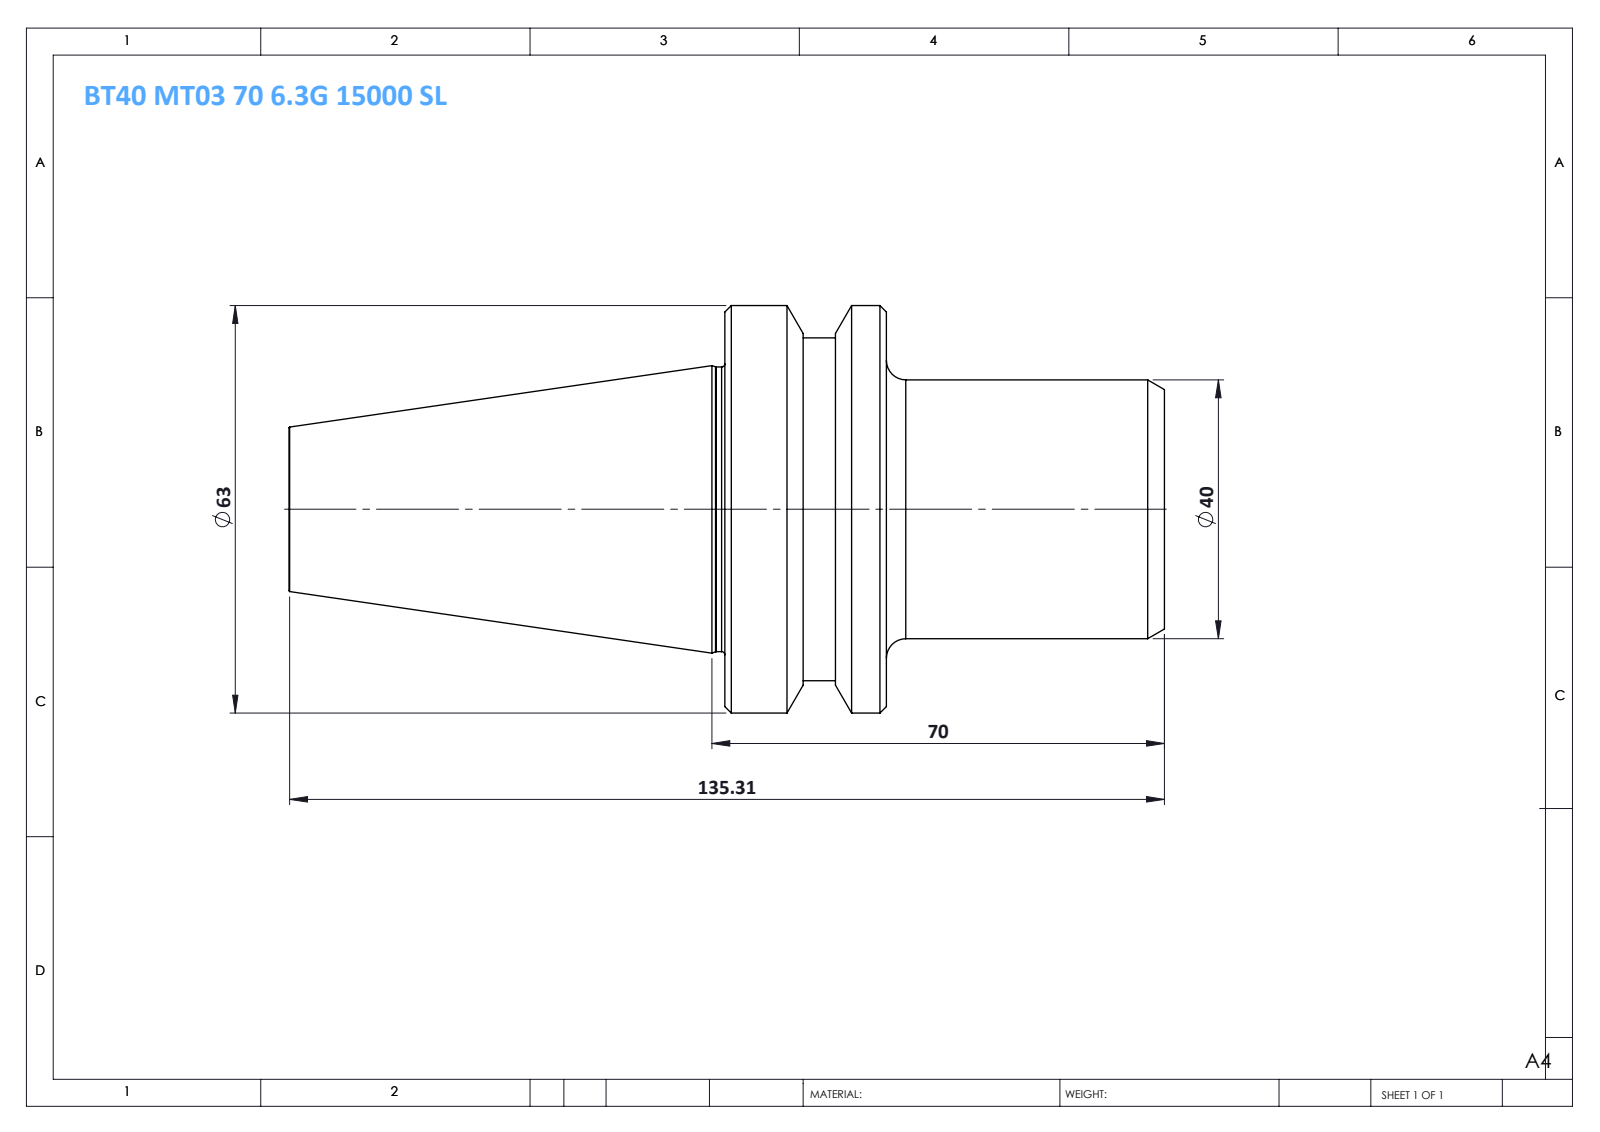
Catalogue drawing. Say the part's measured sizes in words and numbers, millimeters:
The part is named "BT40 MT03 070 6.3G 15000 SL". Its 3-D file was written by "SolidWorks 2014 (CONFIG_CONTROL_DESIGN)". It is 1 solid with 38 faces: 6 planar, 10 cylindrical and 22 other. Overall it measures 135.4 by 63 by 63 millimeters. Its volume is 192 410 cubic millimeters and its surface area 23 455 square millimeters. Round bosses or shafts: 1 of diameter 63, 1 of diameter 53, 1 of diameter 44, 1 of diameter 40. The main face-to-face distances are 25, 43, 68, 135.4, 92.4, 67.4, 55.9, 12.9, 12.1, 79.5.
